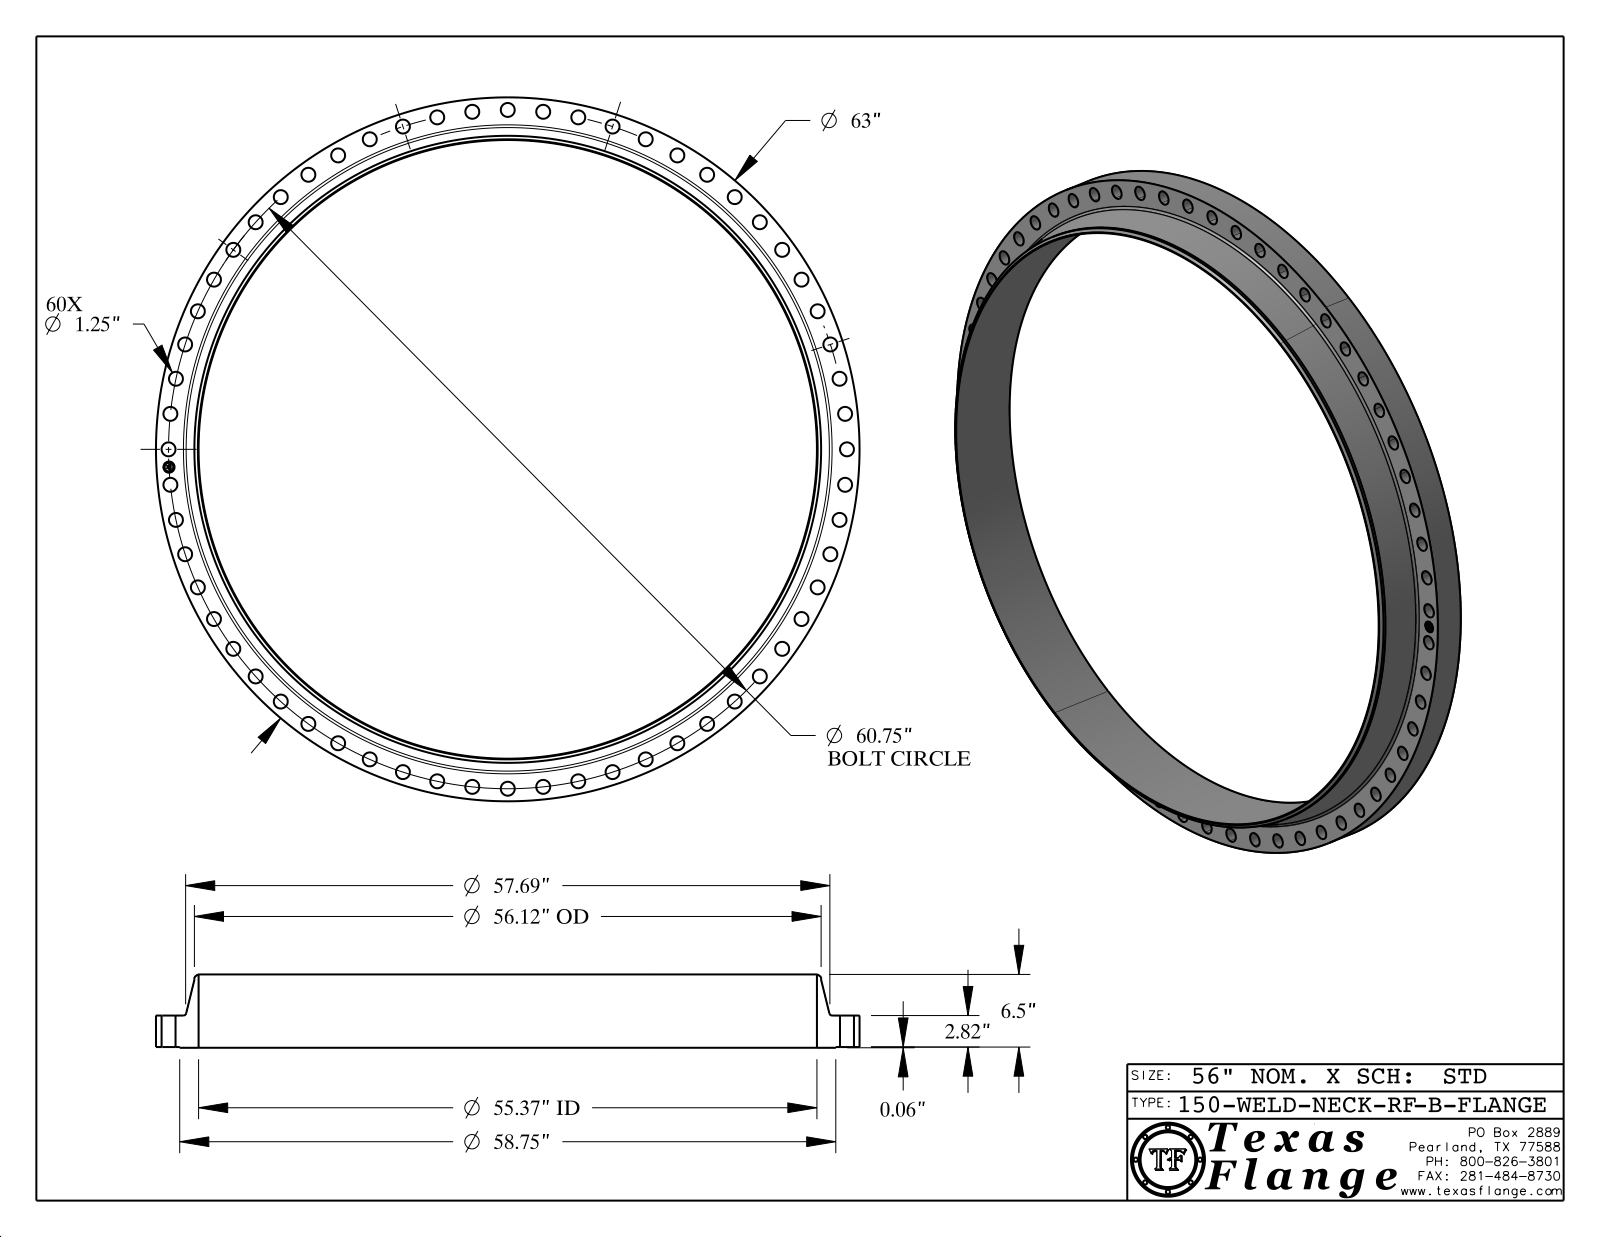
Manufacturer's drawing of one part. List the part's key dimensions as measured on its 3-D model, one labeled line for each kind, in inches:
Part name (STEP PRODUCT): 150-WELD-NECK-RF, Series B
STEP written by: CATIA V5 STEP AP214 (AUTOMOTIVE_DESIGN)
Units: inches
Bodies: 1 solid, 523 faces (369 planar, 148 cylindrical, 6 other)
Overall size (bounding box): 63 × 63 × 6.563
Volume: 2 272 in³ · Surface area: 4 142 in²
Round holes (diameter × count): ⌀1.25 ×60, ⌀1 ×1, ⌀55.37 ×1
Round bosses / shafts (diameter × count): ⌀0.061 ×8, ⌀63 ×1, ⌀58.75 ×1, ⌀56.12 ×1, ⌀0.788 ×1
Main face-to-face distances: 2.82, 0.063, 2.883, 6.563, 6.5, 3.68, 2.868, 2.805, 0.015, 3.695
Hole centre spacings: 15.723, 30.375, 30.375, 6.35, 18.773, 60.002, 60.417, 9.503
